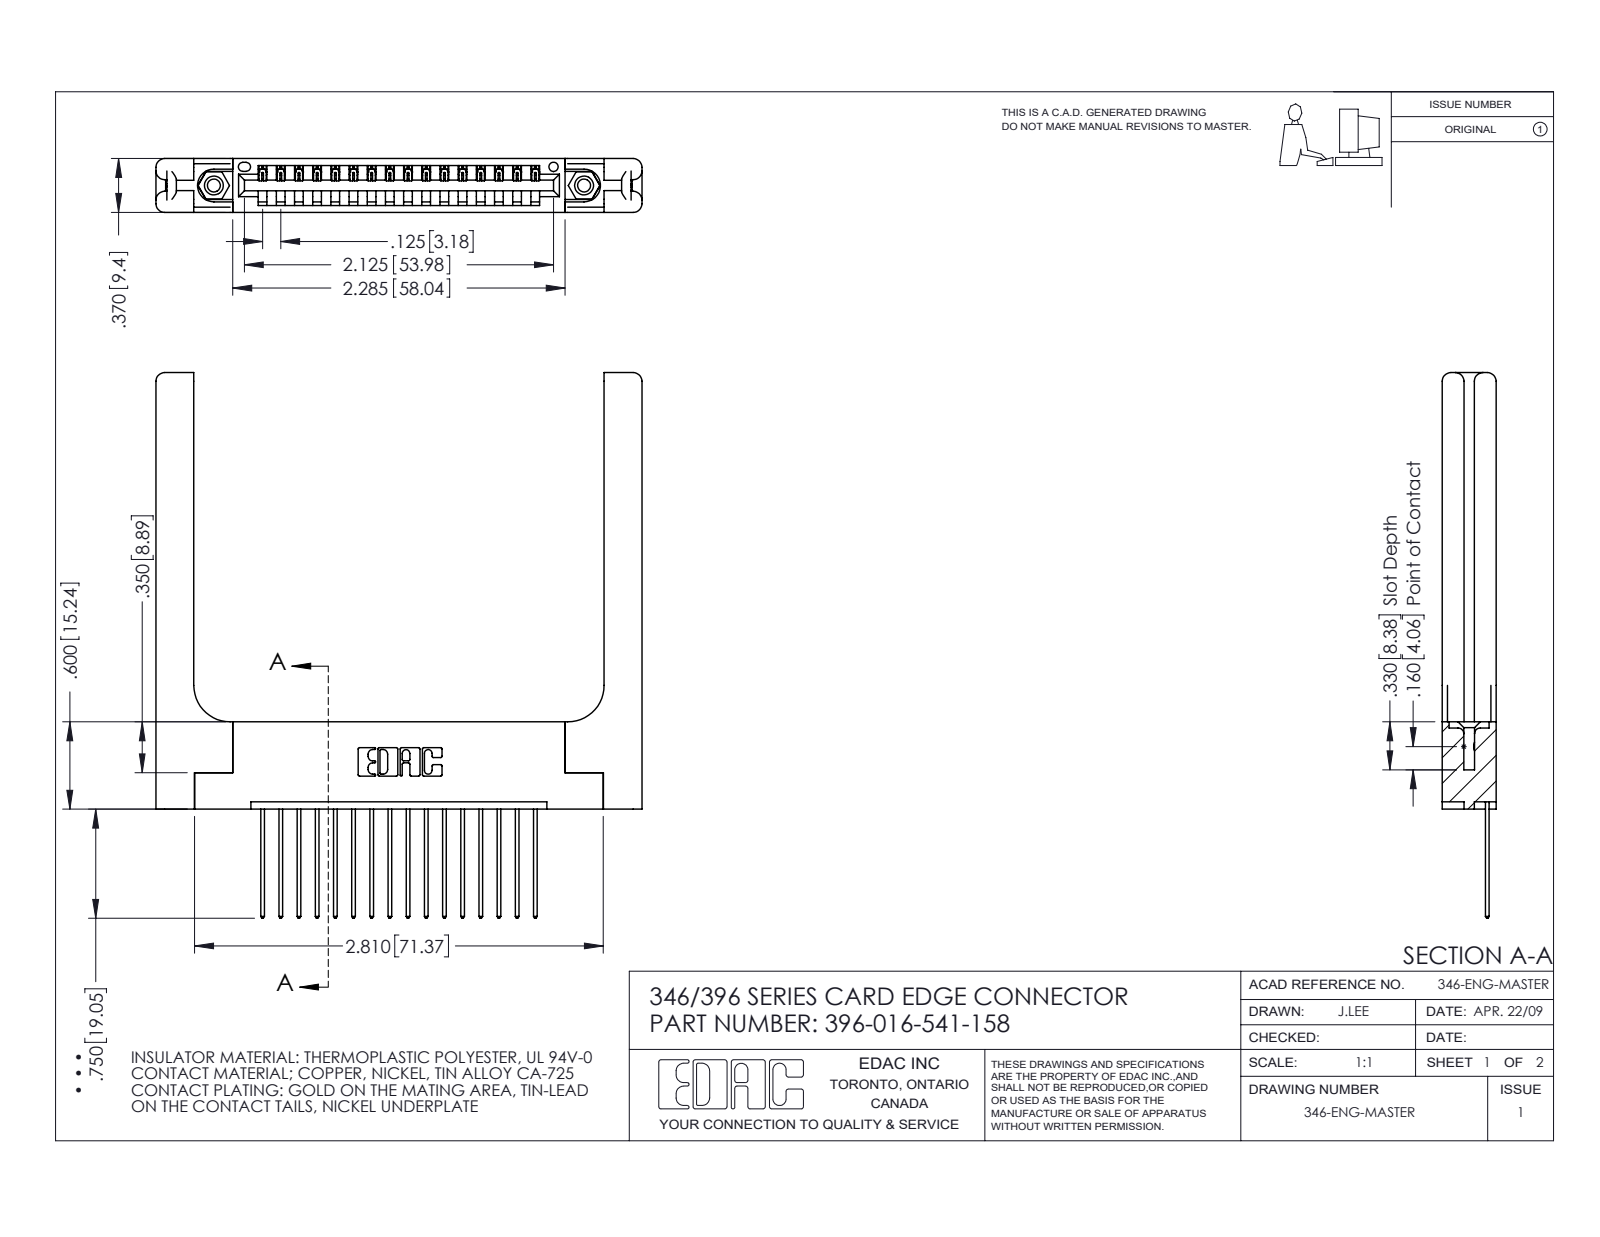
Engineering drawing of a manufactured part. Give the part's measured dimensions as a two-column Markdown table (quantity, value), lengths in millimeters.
| quantity | value |
| --- | --- |
| part name | 346-220-058_345-220-058; 346 Part_Flush Mounting Lugs - 0.156 Dia-TH; 345-292-001_345-293-141; 396-016-541-158 (+1 more) |
| STEP written by | SolidWorks 2016 (CONFIG_CONTROL_DESIGN) |
| units | millimeters |
| bodies | 21 solids, 1306 faces (864 planar, 382 cylindrical, 60 other) |
| overall size | 95.3 × 84.9 × 9.4 |
| volume | 15 500 mm³ |
| surface area | 15 200 mm² |
| round holes (diameter × count) | 2.3 × 2, 3.2 × 2, 4 × 2, 1.6 × 1 |
| round bosses / shafts (diameter × count) | 3.9 × 2 |
| partial cylindrical surfaces (radius × count) | 0.2 × 32, 0.3 × 32, 0.3 × 22, 1.5 × 16, 0.2 × 6, 0.8 × 6, 0.7 × 3, 0.8 × 2 |
| main face-to-face distances | 9.4, 1.8, 3.8, 1.2, 8.2, 3.8, 6.4, 2.6, 5.6, 4.4 |
| hole center spacings | 6.2, 59.4, 64.6 |
